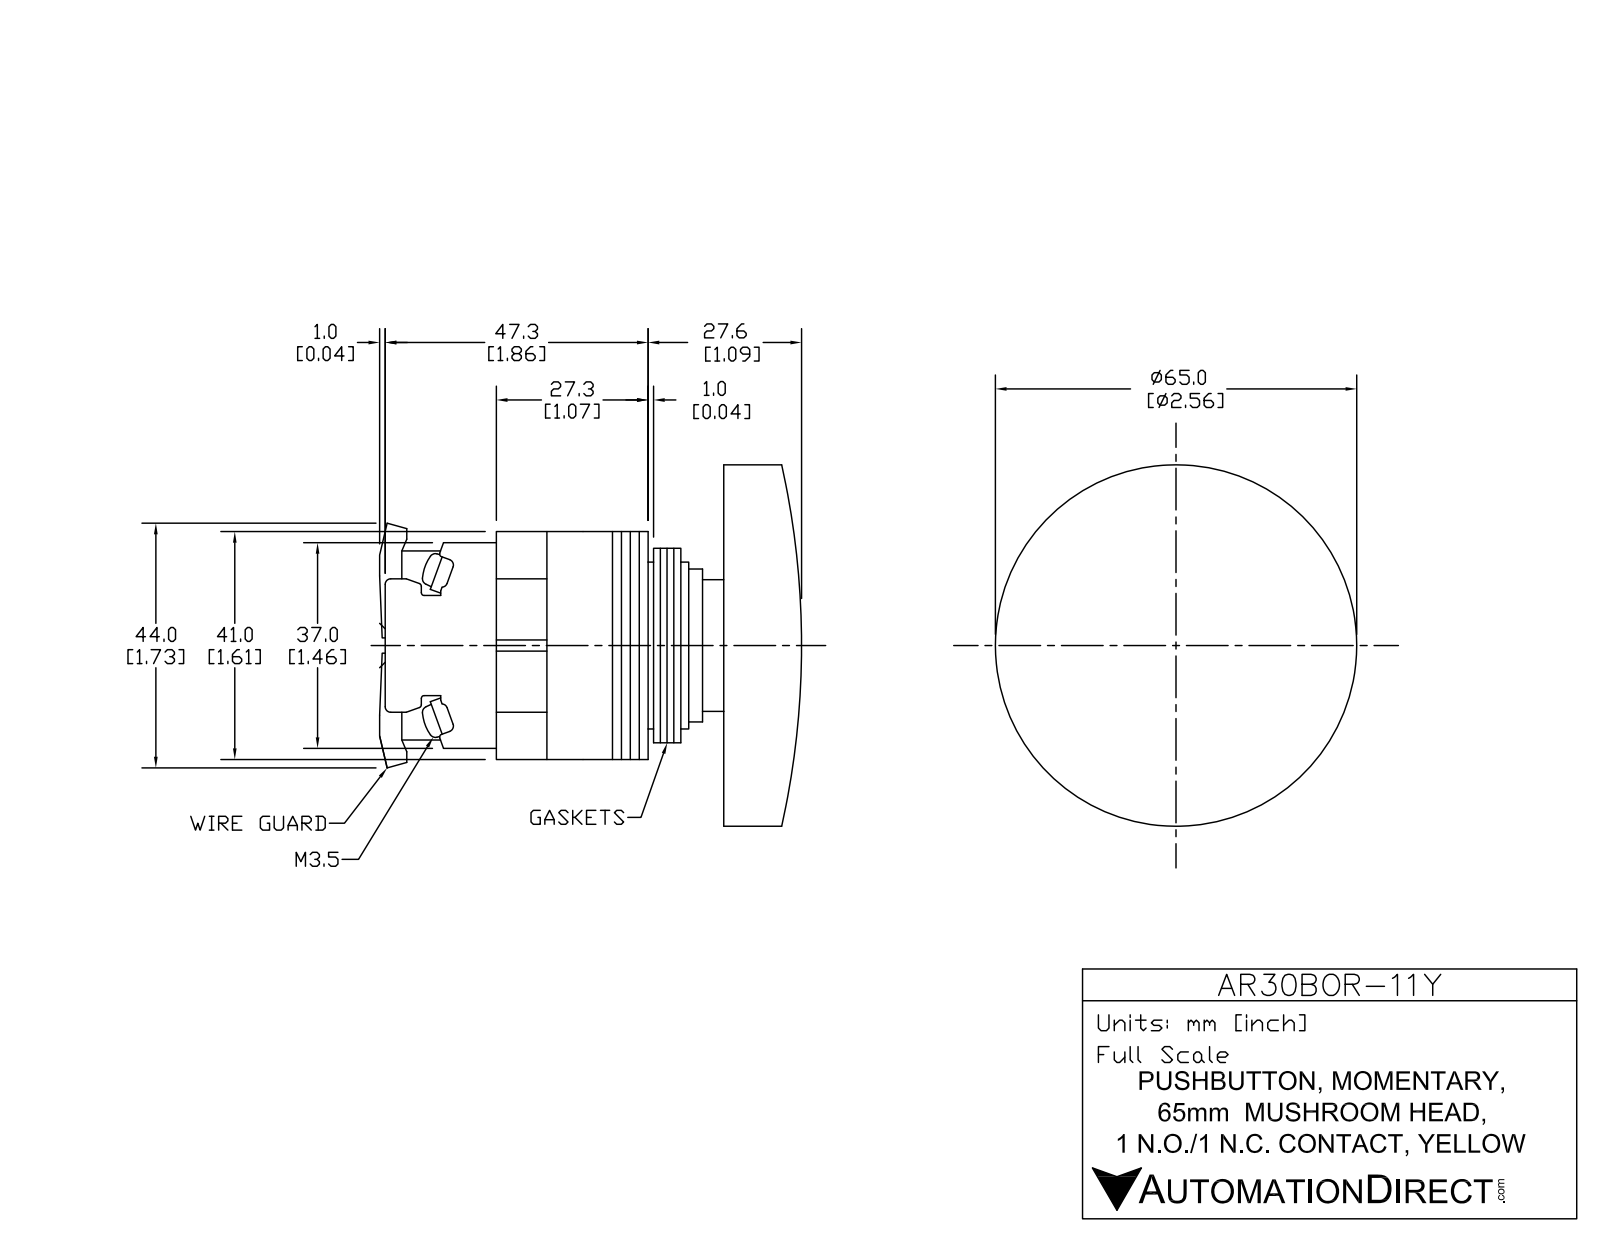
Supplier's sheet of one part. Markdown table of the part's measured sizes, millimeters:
| quantity | value |
| --- | --- |
| part name | AR30B0R-11Y |
| STEP written by | SolidWorks 2017 (AUTOMOTIVE_DESIGN) |
| units | millimeters |
| bodies | 20 solids, 381 faces (236 planar, 127 cylindrical, 18 other) |
| overall size | 76 × 65 × 65 |
| volume | 83 080 mm³ |
| surface area | 42 286 mm² |
| round holes (diameter × count) | 3 × 4, 24 × 1, 30 × 1, 60 × 1 |
| round bosses / shafts (diameter × count) | 5 × 4, 65 × 1, 40 × 1, 35 × 1, 29.8 × 1 |
| partial cylindrical surfaces (radius × count) | 0.5 × 16, 5 × 10, 1.75 × 8, 2 × 4, 3 × 4 |
| main face-to-face distances | 1.6, 21, 16, 3.2, 41, 5, 1, 4.8, 36, 15.99 |
| hole center spacings | 21.92, 31, 43.84 |
